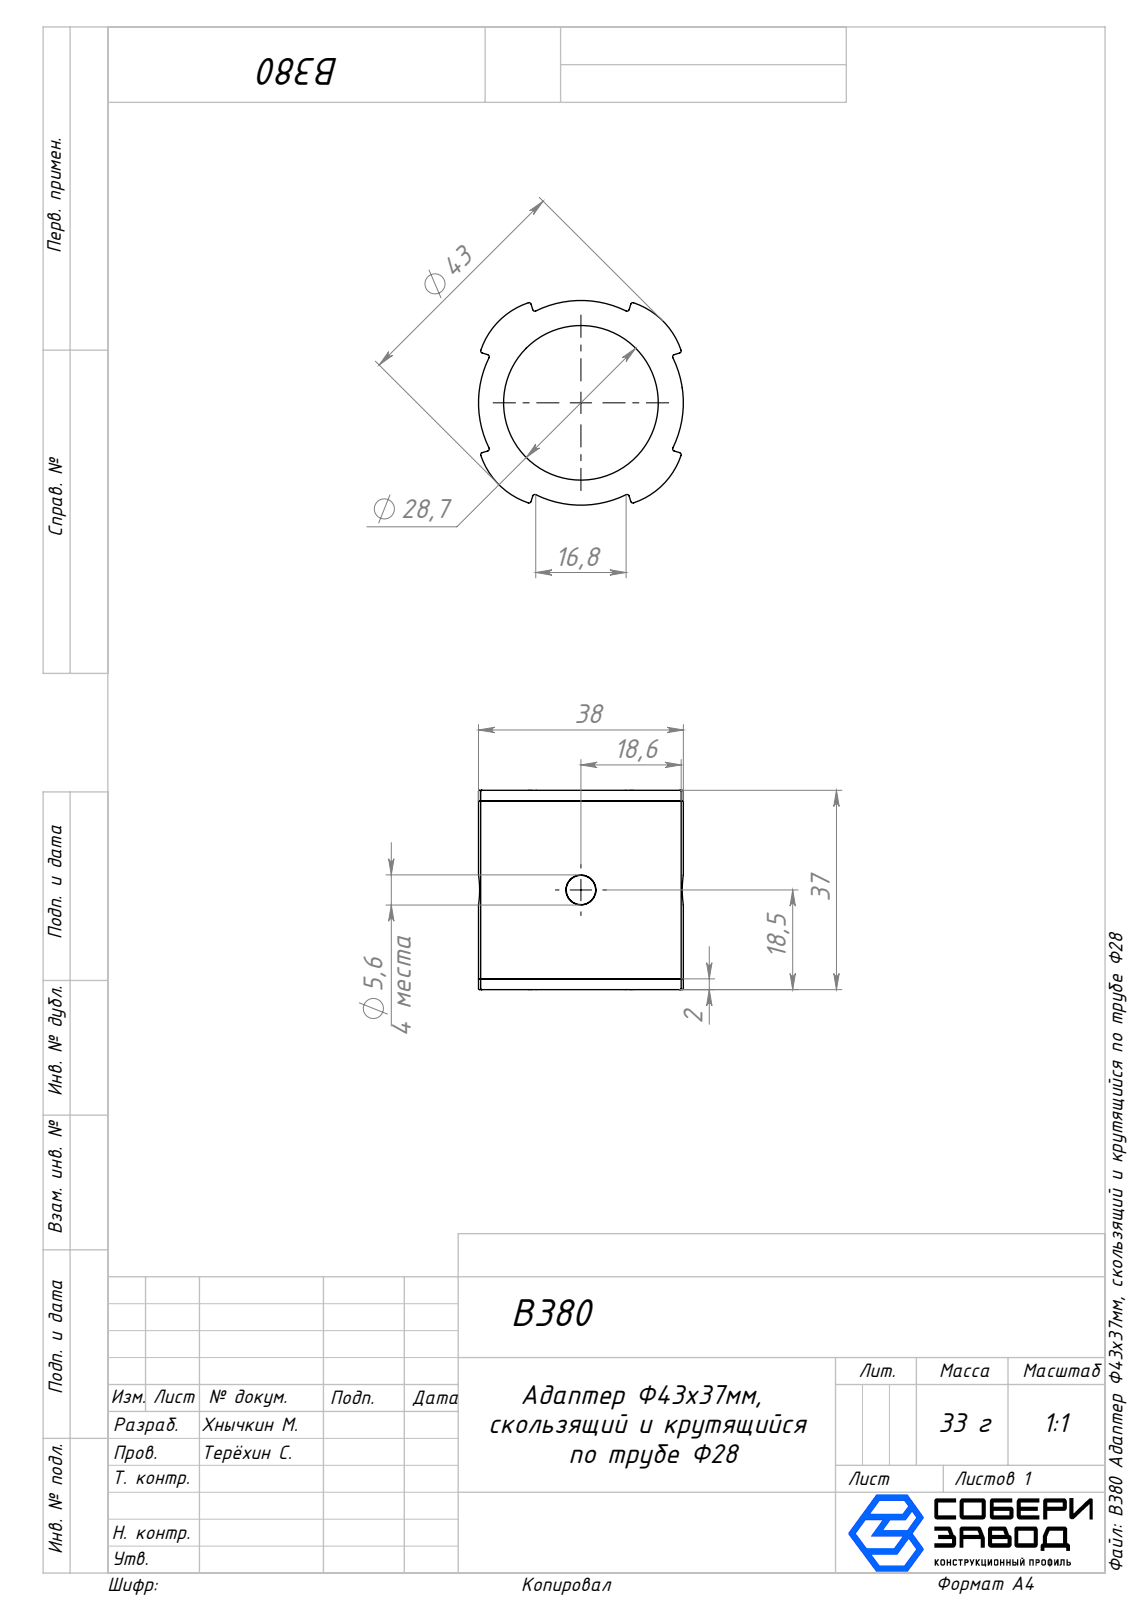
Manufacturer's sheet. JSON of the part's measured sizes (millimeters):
{"part_name": "B380 Адаптер Ф43х37мм, скользящий и крутящийся по трубе Ф28; Крышка_00; Корпус_00", "step_written_by": "SolidWorks 2025 (AUTOMOTIVE_DESIGN)", "units": "millimeters", "bodies": {"solids": 3, "faces": 388, "planar": 97, "cylindrical": 209, "other": 82}, "overall_size": [38, 38, 37], "volume_mm3": 16572, "surface_area_mm2": 18054, "round_holes": [[5.6, 2], [28.7, 1], [30, 1]], "round_bosses_or_shafts": [[33.6, 1]], "partial_cylinders_radius": [[0.5, 24], [0.2, 16], [0.4, 16], [1, 16], [14, 4], [16.8, 4], [17, 1], [19, 1]], "face_to_face_distances": [2, 35, 33, 37, 11, 9.5, 13, 24, 22, 20.59]}
